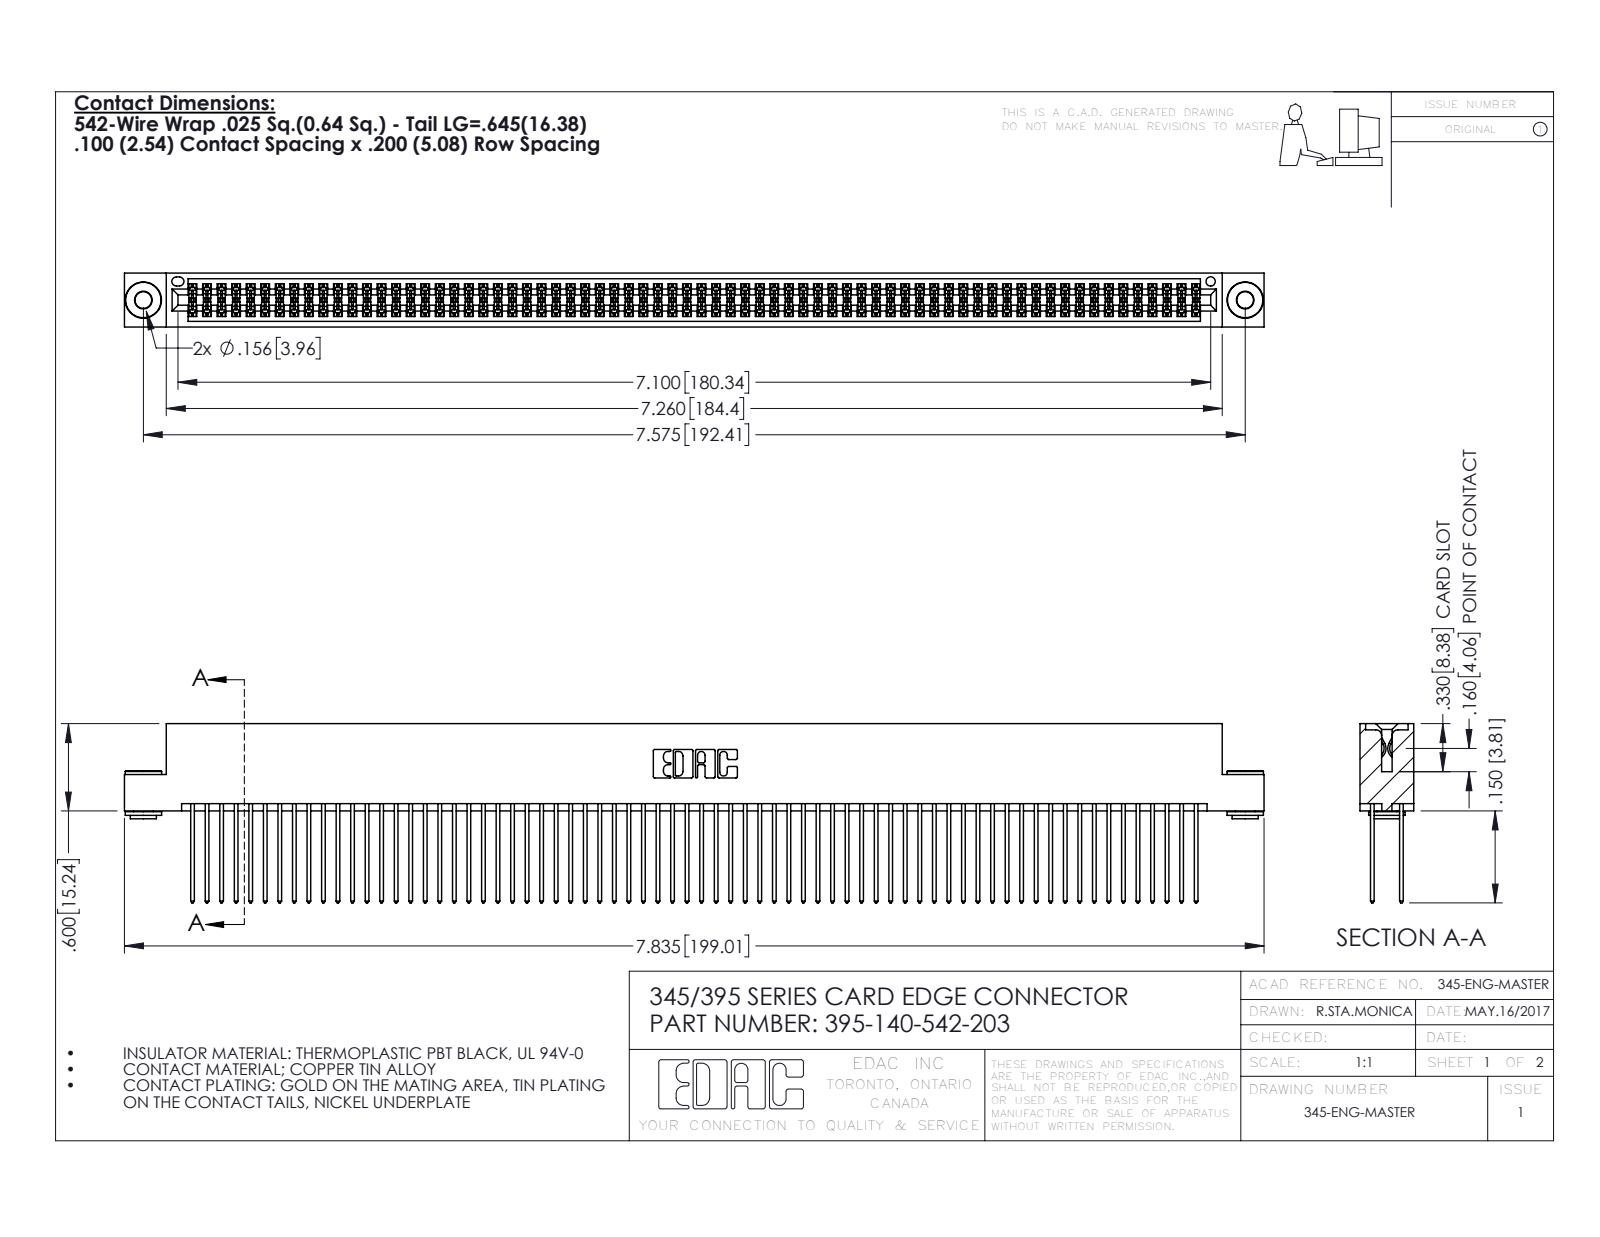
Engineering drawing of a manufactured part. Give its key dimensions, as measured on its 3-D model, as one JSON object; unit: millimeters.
{"part_name": "395-140-542-203; 345-292-001_345-293-142; 345-250-002_345-250-002-102; 345 Part_Flush Mounting Lugs - 0.156 Dia-TH", "step_written_by": "SolidWorks 2016 (CONFIG_CONTROL_DESIGN)", "units": "millimeters", "bodies": {"solids": 143, "faces": 7164, "planar": 4710, "cylindrical": 2446, "other": 8}, "overall_size": [199, 31.3, 9.4], "volume_mm3": 20270, "surface_area_mm2": 33750, "round_holes": [[2.9, 2], [4, 2], [1.6, 1]], "round_bosses_or_shafts": [[6.4, 2], [4.6, 2], [3.5, 2]], "partial_cylinders_radius": [[0.2, 210], [0.3, 140], [0.3, 22], [0.2, 6], [0.8, 6], [0.7, 3], [0.4, 2], [0.5, 2]], "face_to_face_distances": [1.8, 7.6, 5.1, 0.6, 2.5, 6.9, 5.7, 9.4, 4.4, 3.8], "hole_center_spacings": [6.9, 186.4, 192.4]}
